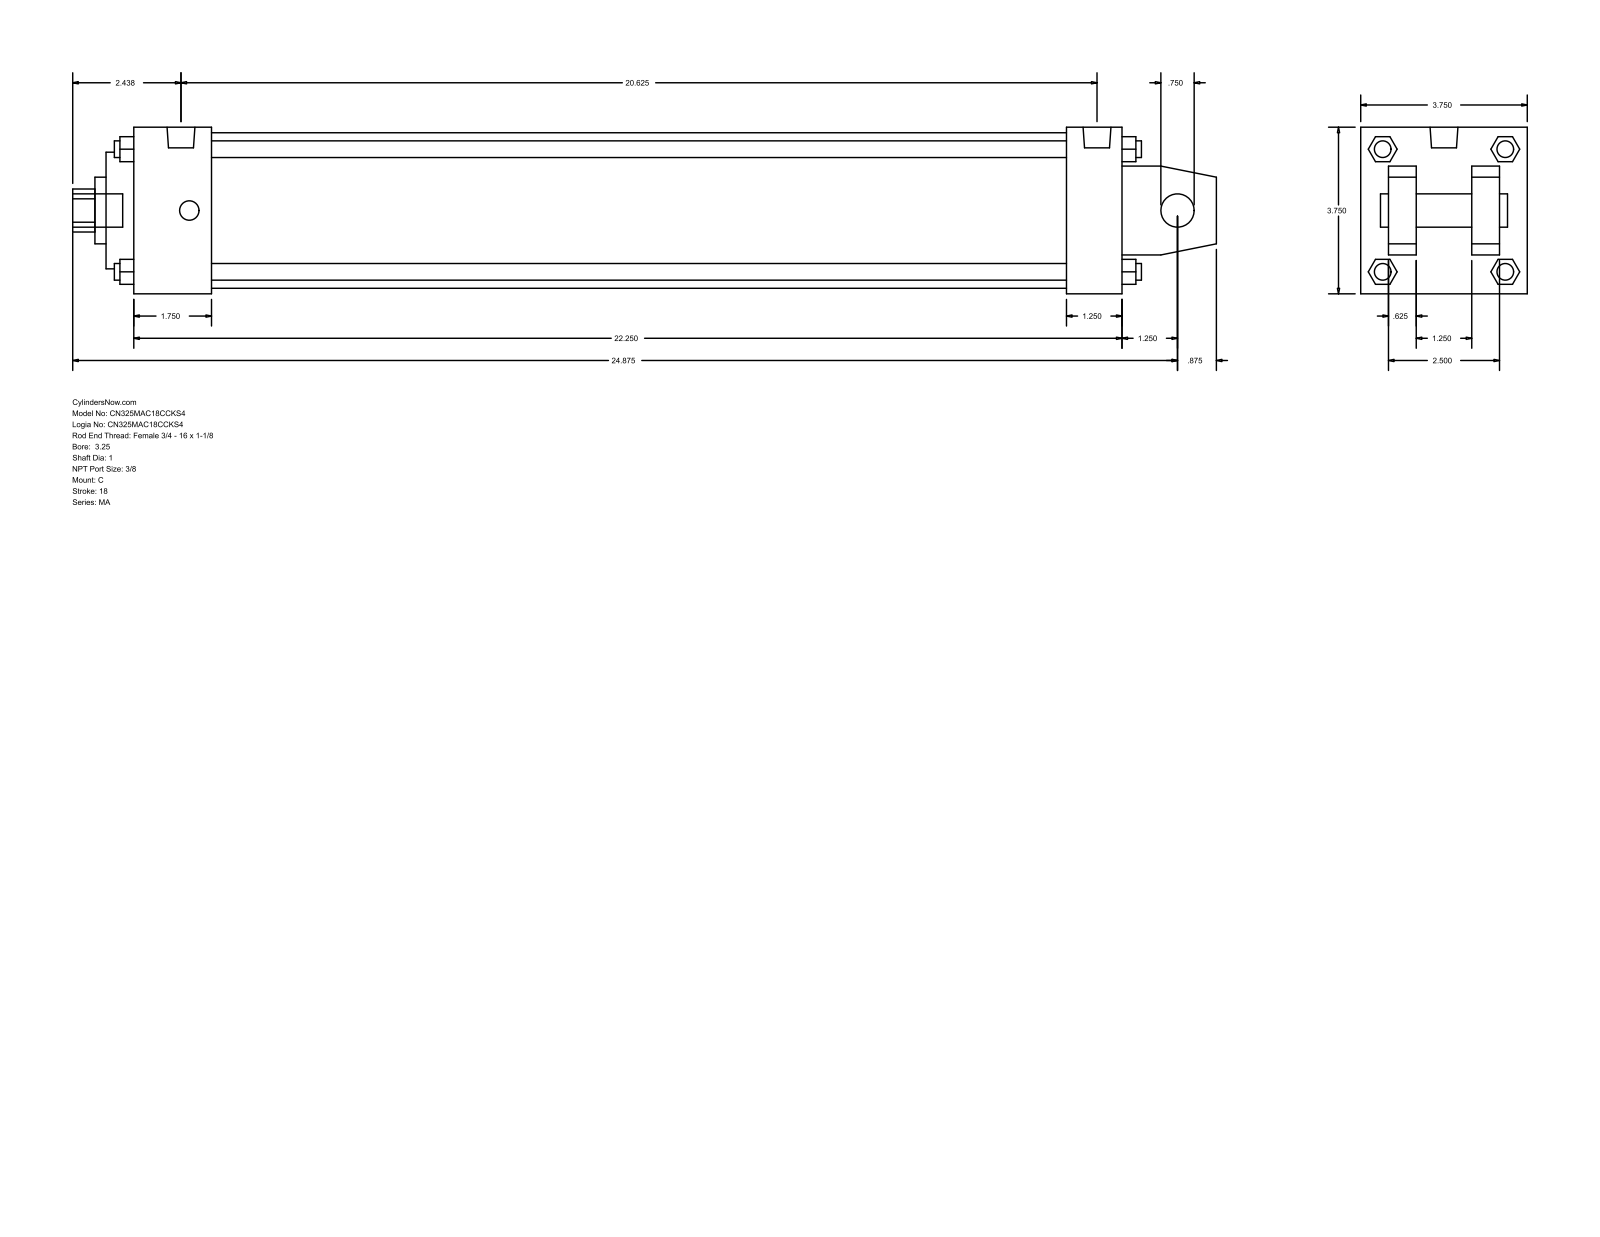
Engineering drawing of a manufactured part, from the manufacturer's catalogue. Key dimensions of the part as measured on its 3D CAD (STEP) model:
Part name (STEP PRODUCT): MA_C__0325_1
STEP written by: GSSL Pune (CONFIG_CONTROL_DESIGN)
Units: millimetres
Bodies: 0 solids, 141 faces (109 planar, 32 cylindrical, 0 other)
Overall size (bounding box): 654.05 × 95.25 × 95.25
Round holes (diameter × count): ⌀19.05 ×1, ⌀25.4 ×1, ⌀38.1 ×1, ⌀66.67 ×1, ⌀88.9 ×1
Round bosses / shafts (diameter × count): ⌀11.11 ×4, ⌀9.53 ×4, ⌀15.93 ×2, ⌀19.05 ×1
Partial cylindrical surfaces — rounded edges, fillets, slot ends (radius × count): R12.29 ×1
Main face-to-face distances: 95.24, 15.87, 63.5, 565.16, 31.74, 79.37, 47.63, 533.41, 31.75, 44.46
